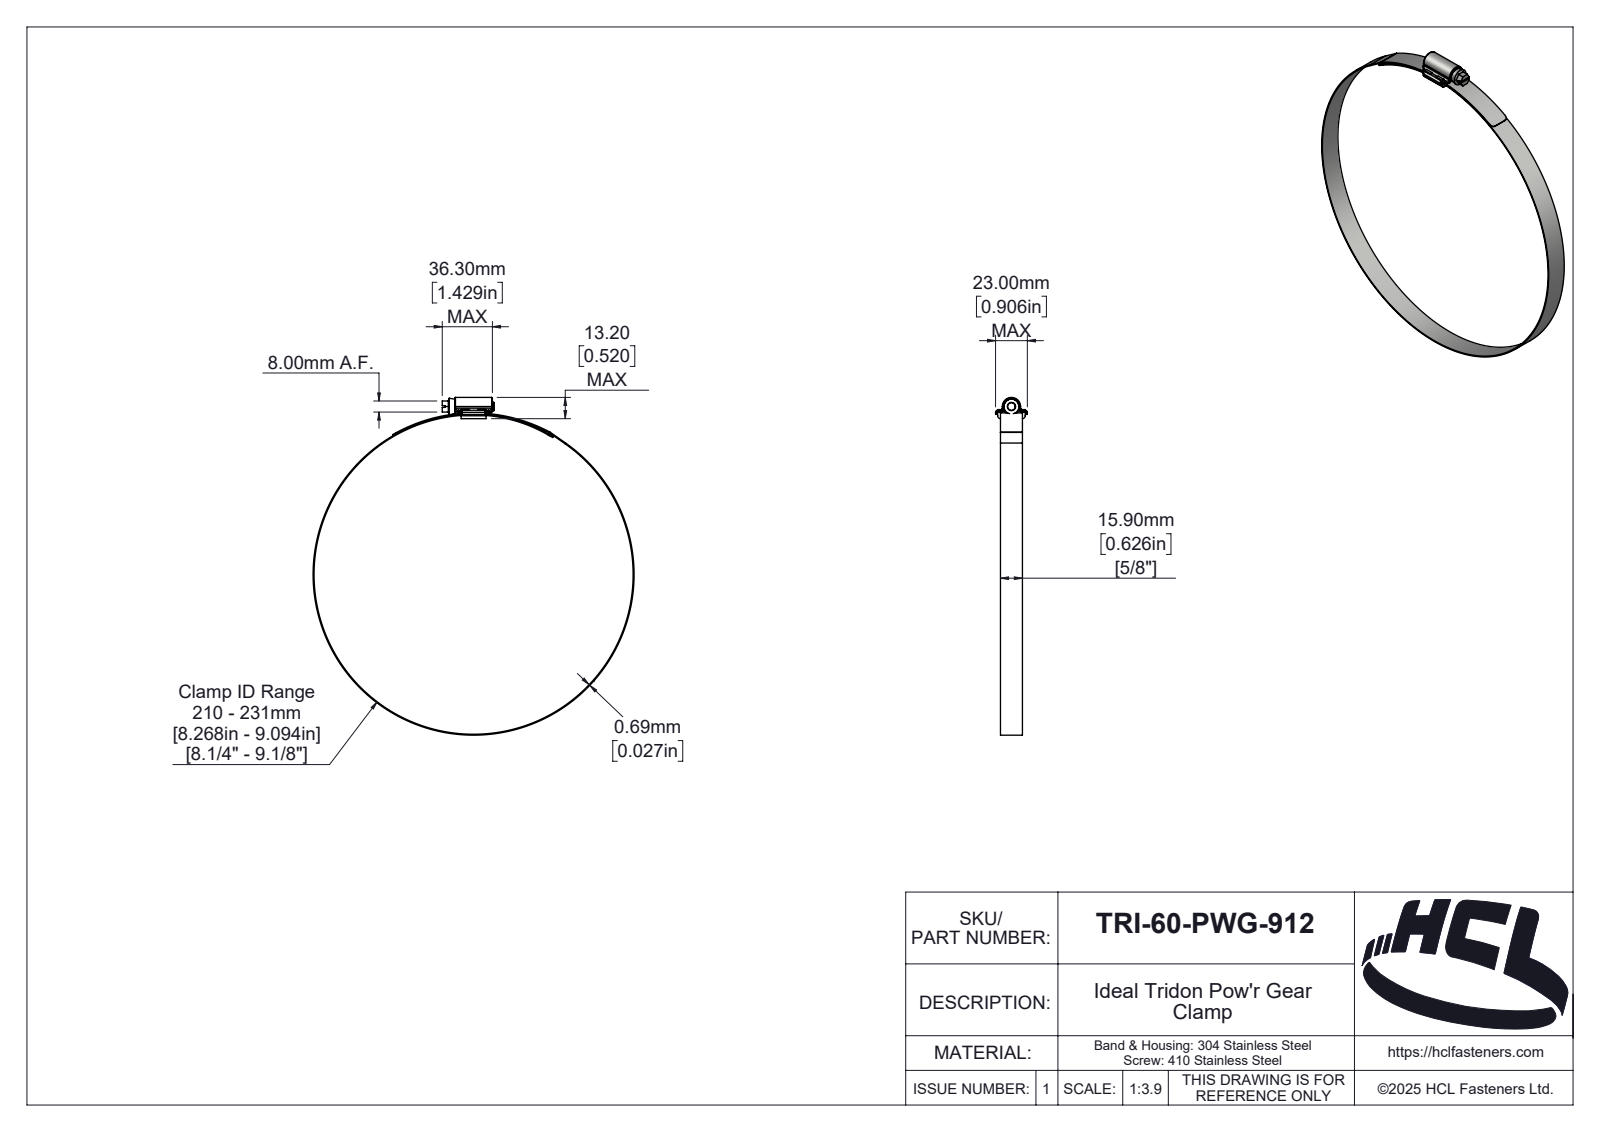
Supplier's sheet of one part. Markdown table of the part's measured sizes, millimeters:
| quantity | value |
| --- | --- |
| part name | TRI-60-PWG-912 |
| STEP written by | SolidWorks 2025 (AUTOMOTIVE_DESIGN) |
| units | millimeters |
| bodies | 4 solids, 268 faces (87 planar, 102 cylindrical, 79 other) |
| overall size | 244.39 × 232.38 × 23 |
| volume | 14 516 mm³ |
| surface area | 32 799 mm² |
| round holes (diameter × count) | 231 × 1 |
| round bosses / shafts (diameter × count) | 232.38 × 1, 10.7 × 1, 6 × 1 |
| partial cylindrical surfaces (radius × count) | 1 × 14, 0.5 × 4, 1.5 × 4, 2 × 3, 0.1 × 2, 2.1 × 2, 3 × 2, 0.46 × 1 |
| main face-to-face distances | 15.9, 2, 0.69, 17.9, 4.9, 1.2, 4.55, 3.35, 15.35, 2.55 |
